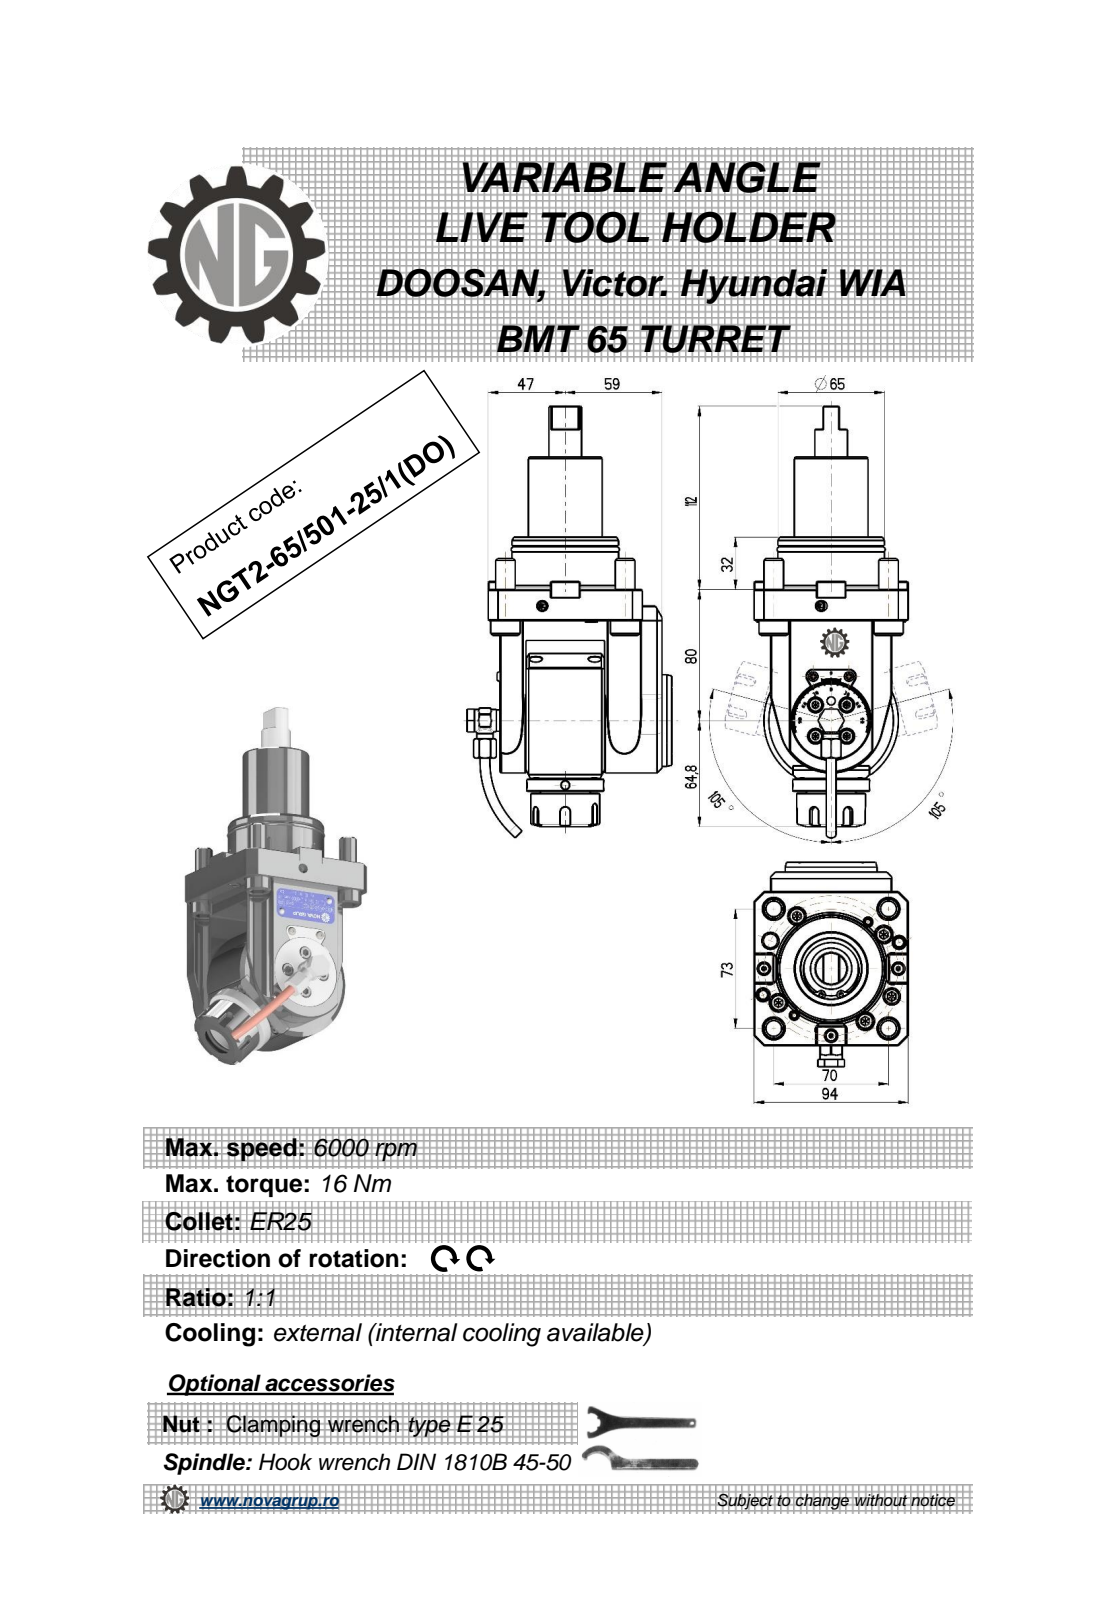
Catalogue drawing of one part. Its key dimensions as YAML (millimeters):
part_name: "NGT2_65_501_25_1_DO"
step_written_by: "PRO/ENGINEER BY PARAMETRIC TECHNOLOGY CORPORATION, 2010280 (CONFIG_CONTROL_DESIGN)"
units: millimeters
bodies: {solids: 2, faces: 635, planar: 273, cylindrical: 178, other: 184}
overall_size: [263.67, 124.9, 94]
volume: 992545
surface_area: 102638
round_holes:
  - {diameter: 4, count: 3}
  - {diameter: 5, count: 2}
  - {diameter: 8.5, count: 2}
  - {diameter: 3, count: 1}
  - {diameter: 6.2, count: 1}
  - {diameter: 9, count: 1}
  - {diameter: 11, count: 1}
  - {diameter: 20.3, count: 1}
round_bosses_or_shafts:
  - {diameter: 18, count: 4}
  - {diameter: 12, count: 4}
  - {diameter: 10, count: 2}
  - {diameter: 8, count: 2}
  - {diameter: 6, count: 2}
  - {diameter: 5.7, count: 2}
  - {diameter: 82, count: 1}
  - {diameter: 65, count: 1}
partial_cylinders:
  - {radius: 0.36, count: 20}
  - {radius: 0.41, count: 12}
  - {radius: 0.51, count: 6}
  - {radius: 10, count: 6}
  - {radius: 3, count: 5}
  - {radius: 0.5, count: 4}
  - {radius: 0.8, count: 2}
  - {radius: 1, count: 2}
face_to_face_distances: [31, 12, 10, 99, 23, 112, 84, 6, 94, 71]
hole_center_spacings: [40.72, 0.4, 39.45, 48.92, 49, 49.18, 49.4, 75.66]
